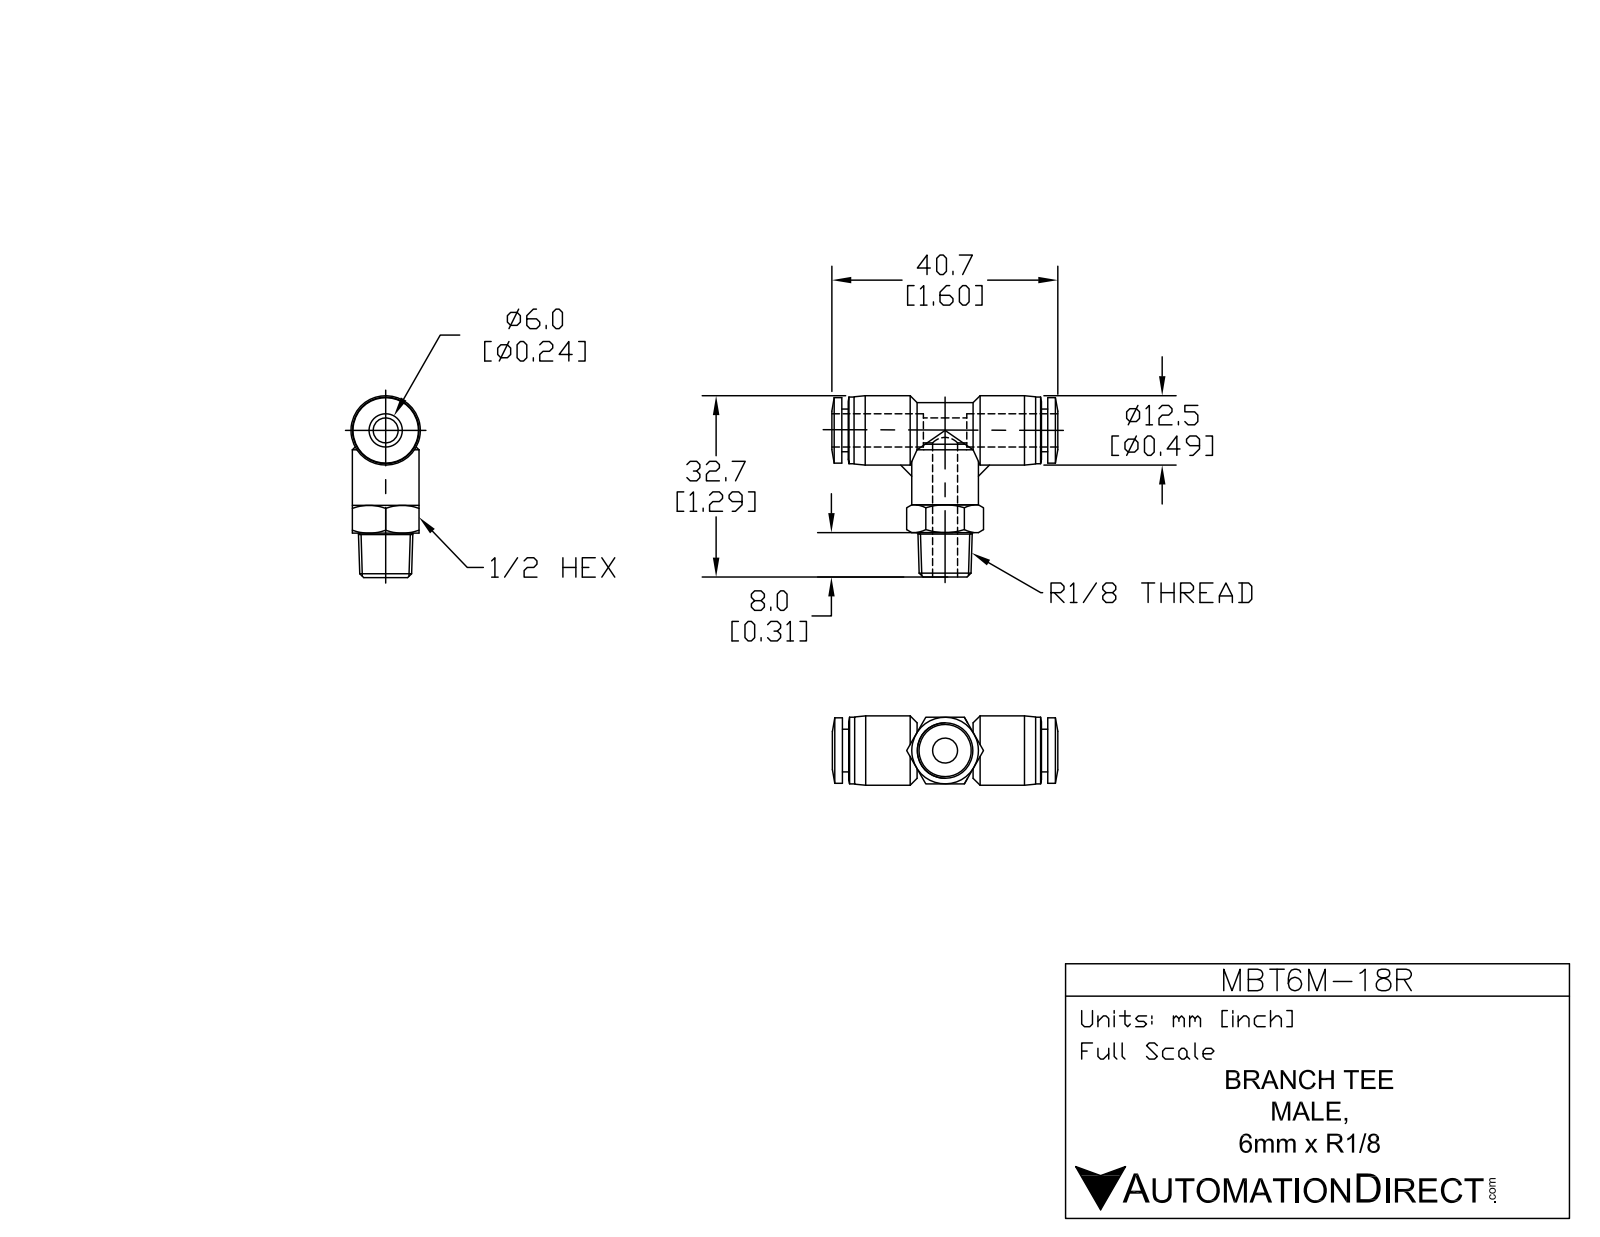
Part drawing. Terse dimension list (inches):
name: MBT6M-18R
written by: SolidWorks 2015 (AUTOMOTIVE_DESIGN)
unit: in
bodies: 1 solid, 93 faces (24 planar, 31 cylindrical, 38 other)
size: 1.598 × 1.289 × 0.492
volume: 0.303 in³; area: 5.835 in²
holes: 2× ⌀0.157, 1× ⌀0.248
bosses: 2× ⌀0.472, 1× ⌀0.492, 1× ⌀0.465, 1× ⌀0.303
rounds: 2× R0.187
face distances: 0.472, 0.045, 1.411, 1.457, 1.366, 0.575, 0.882, 0.53, 0.837, 0.315
